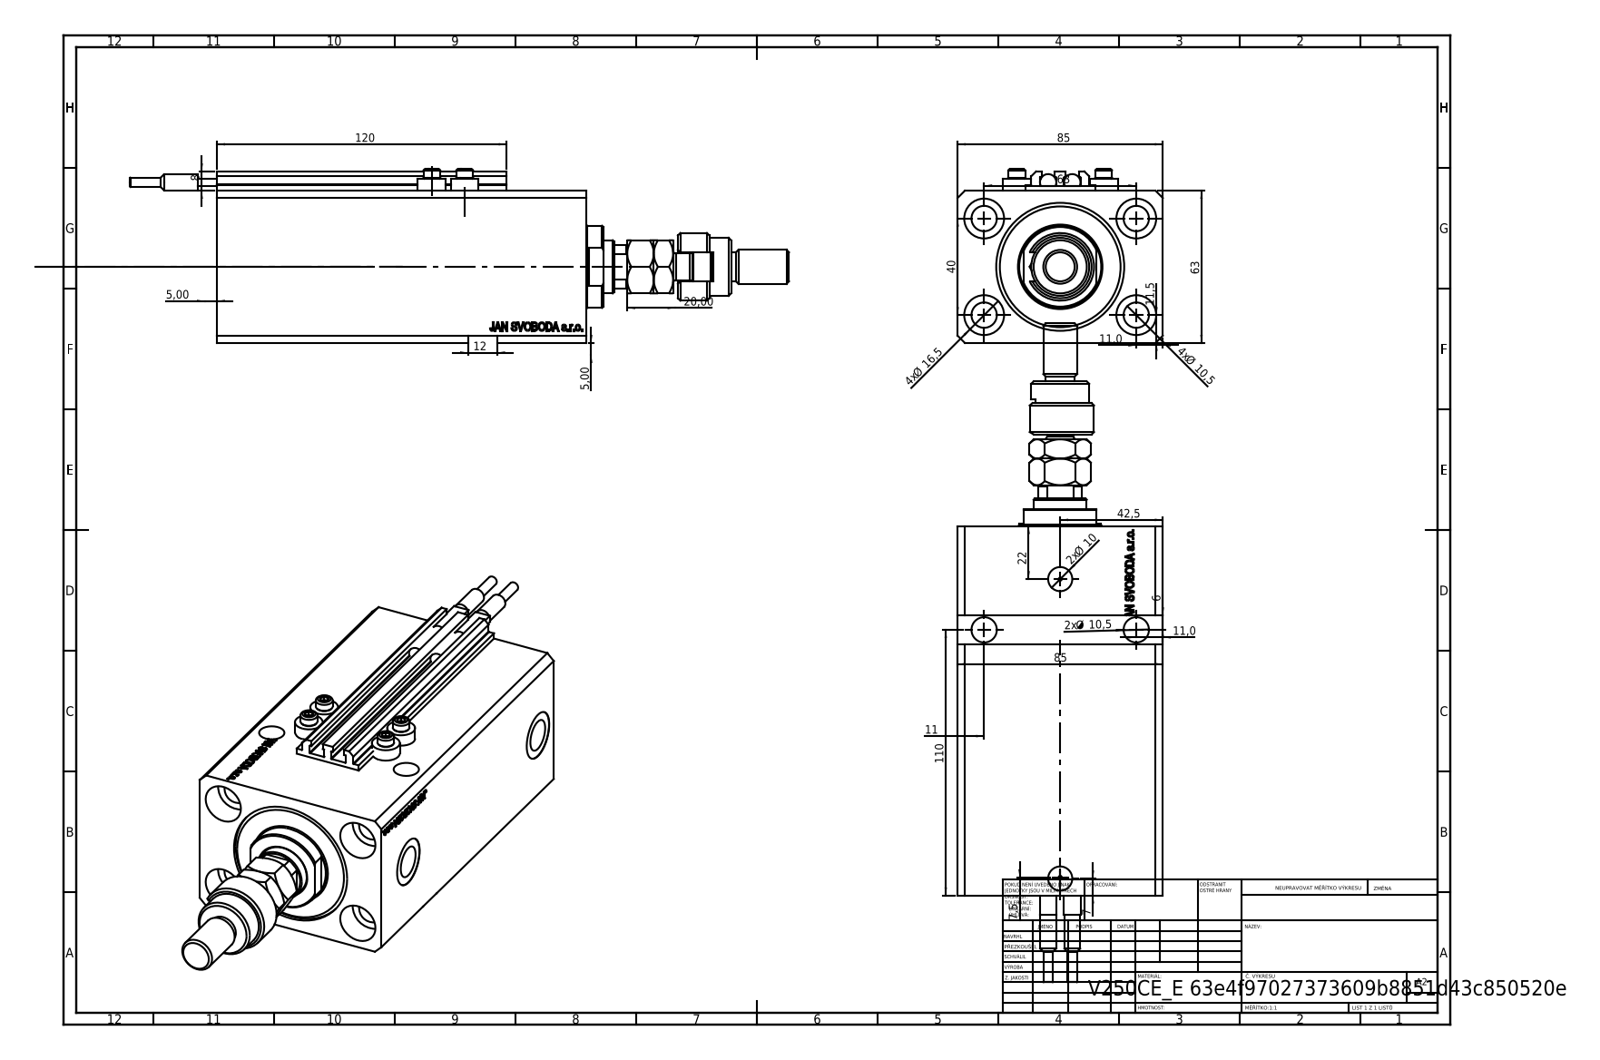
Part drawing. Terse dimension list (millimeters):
name: V250CE_E_Body; V250CE_VC_E; ALLEN BOLT V250CE; MFA (+3 more)
written by: SolidWorks 2019 (CONFIG_CONTROL_DESIGN)
unit: mm
bodies: 12 solids, 1224 faces (595 planar, 151 cylindrical, 478 other)
size: 272.9 × 85 × 72
volume: 717 137 mm³; area: 151 651 mm²
holes: 6× ⌀10.5, 4× ⌀1.25, 4× ⌀4, 4× ⌀16.5, 2× ⌀10, 2× ⌀13.16, 2× ⌀20, 1× ⌀12.5, 1× ⌀22, 1× ⌀40, 1× ⌀53
bosses: 4× ⌀11.6, 4× ⌀7, 2× ⌀6.8, 2× ⌀6.5, 2× ⌀4, 1× ⌀34, 1× ⌀28, 1× ⌀24
rounds: 10× R0.2, 1× R9.75, 1× R10.5
face distances: 63, 85, 153, 65, 125.9, 27.1, 3, 11.4, 114.5, 141.6
hole spacings: 37.31, 63, 13.6, 15.4, 24.96, 33.62, 36, 37.86
